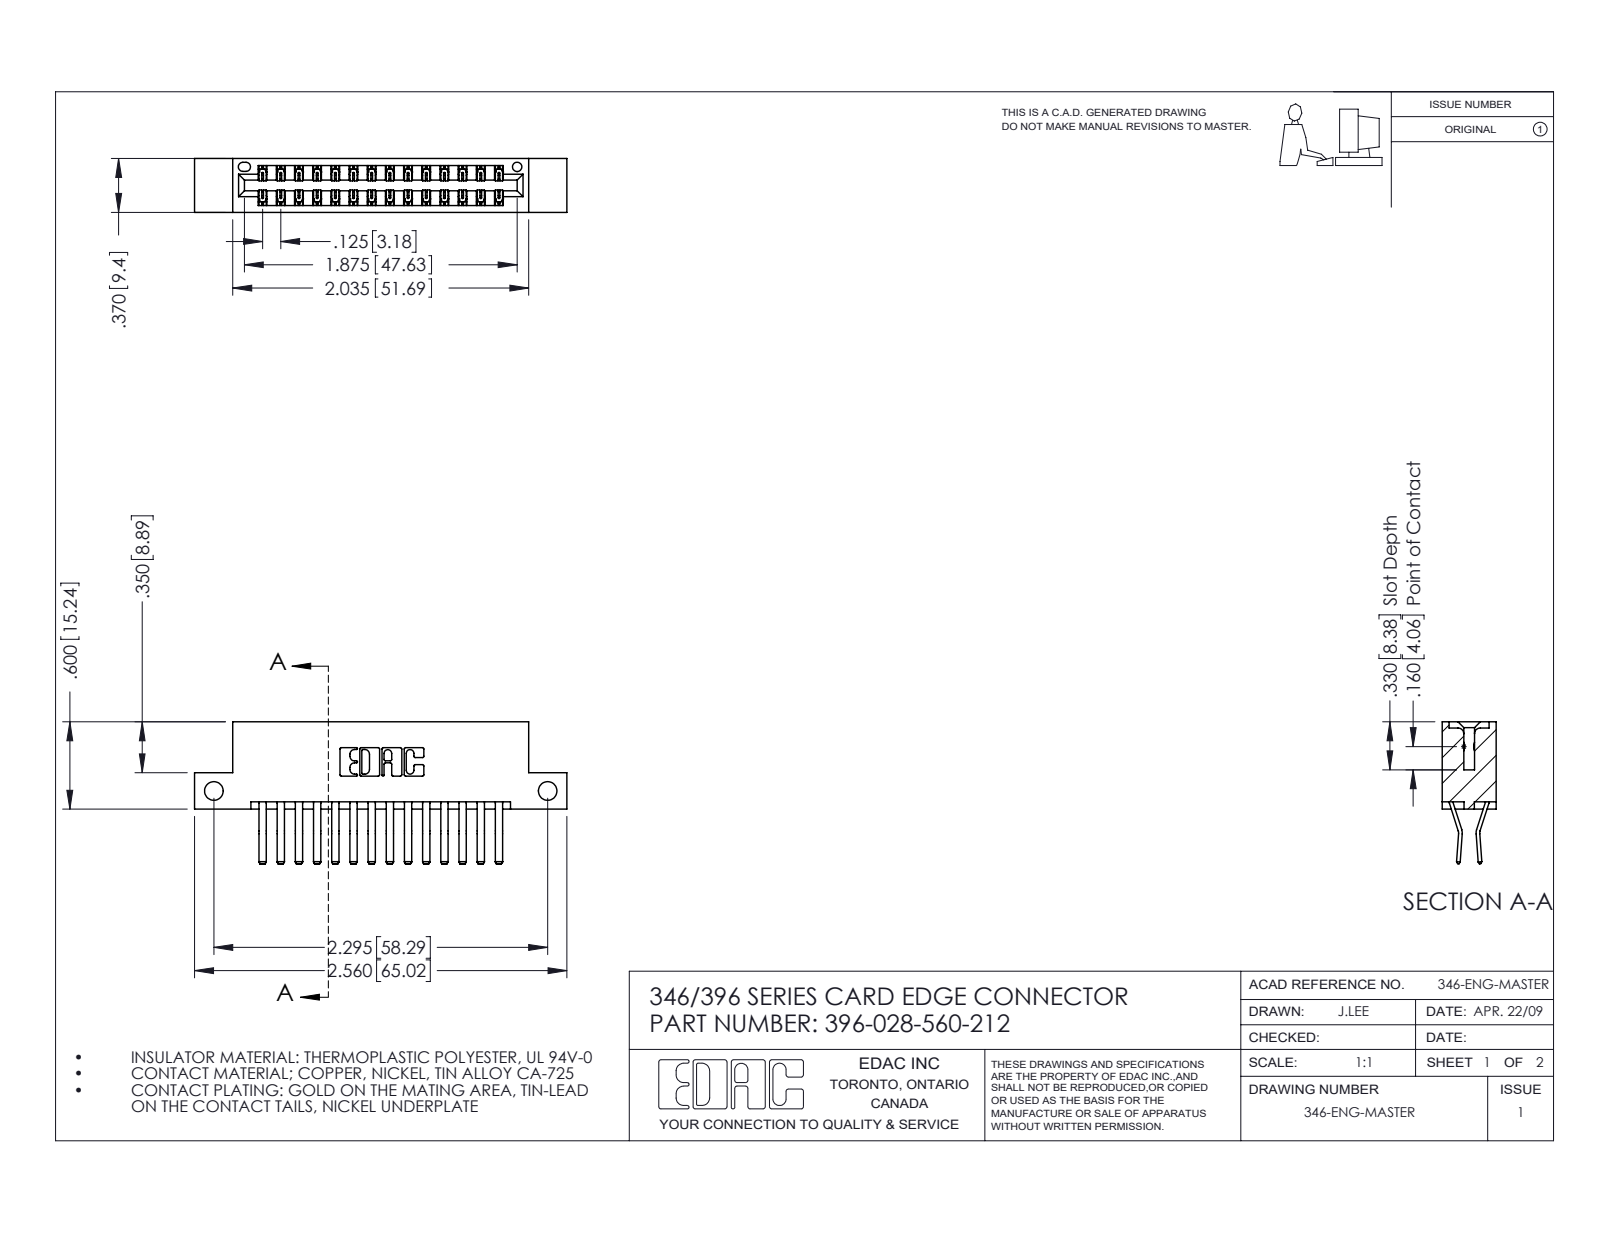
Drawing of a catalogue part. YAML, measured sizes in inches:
part_name: "396-028-560-212; 346 Part_Flush Mounting Lugs - Side Mount; 345-292-001_560 Tail"
step_written_by: "SolidWorks 2016 (CONFIG_CONTROL_DESIGN)"
units: inches
bodies: {solids: 29, faces: 1634, planar: 1056, cylindrical: 578, other: 0}
overall_size: [2.56, 0.975, 0.37]
volume: 0.38
surface_area: 13.11
round_holes:
  - {diameter: 0.128, count: 2}
  - {diameter: 0.064, count: 1}
partial_cylinders:
  - {radius: 0.006, count: 42}
  - {radius: 0.01, count: 22}
  - {radius: 0.007, count: 6}
  - {radius: 0.031, count: 6}
  - {radius: 0.026, count: 3}
  - {radius: 0.01, count: 2}
  - {radius: 0.014, count: 2}
  - {radius: 0.022, count: 2}
face_to_face_distances: [0.25, 0.048, 0.322, 0.37, 0.025, 0.072, 0.298, 0.275, 0.148, 0.222]
hole_center_spacings: [2.295]
